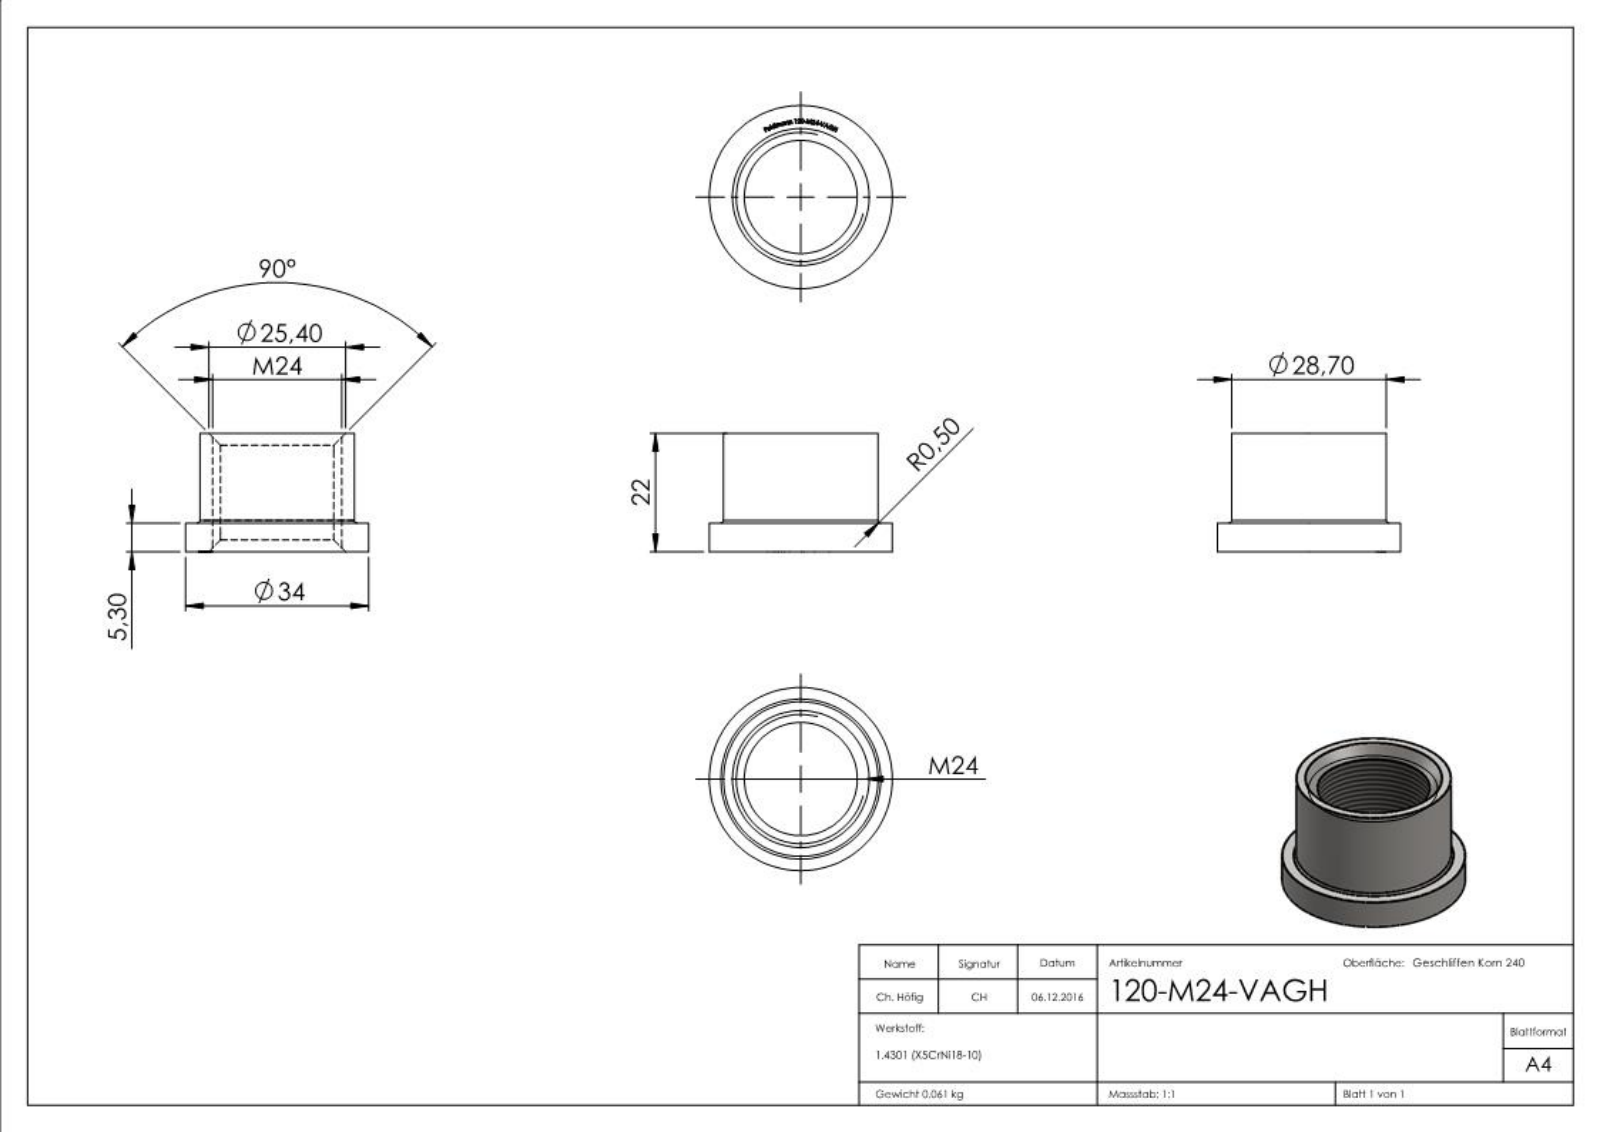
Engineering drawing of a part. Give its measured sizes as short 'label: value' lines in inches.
name: 120-M24-VAGH
written by: SolidWorks 2015 (CONFIG_CONTROL_DESIGN)
unit: in
bodies: 1 solid, 259 faces (169 planar, 6 cylindrical, 84 other)
size: 1.339 × 1.339 × 0.866
volume: 0.467 in³; area: 6.939 in²
holes: 1× ⌀0.827
bosses: 1× ⌀1.339, 1× ⌀1.13
face distances: 0.209, 0.866, 0.657, 0.205, 0.862, 0.016, 0.022, 0.019, 0.019, 0.02
